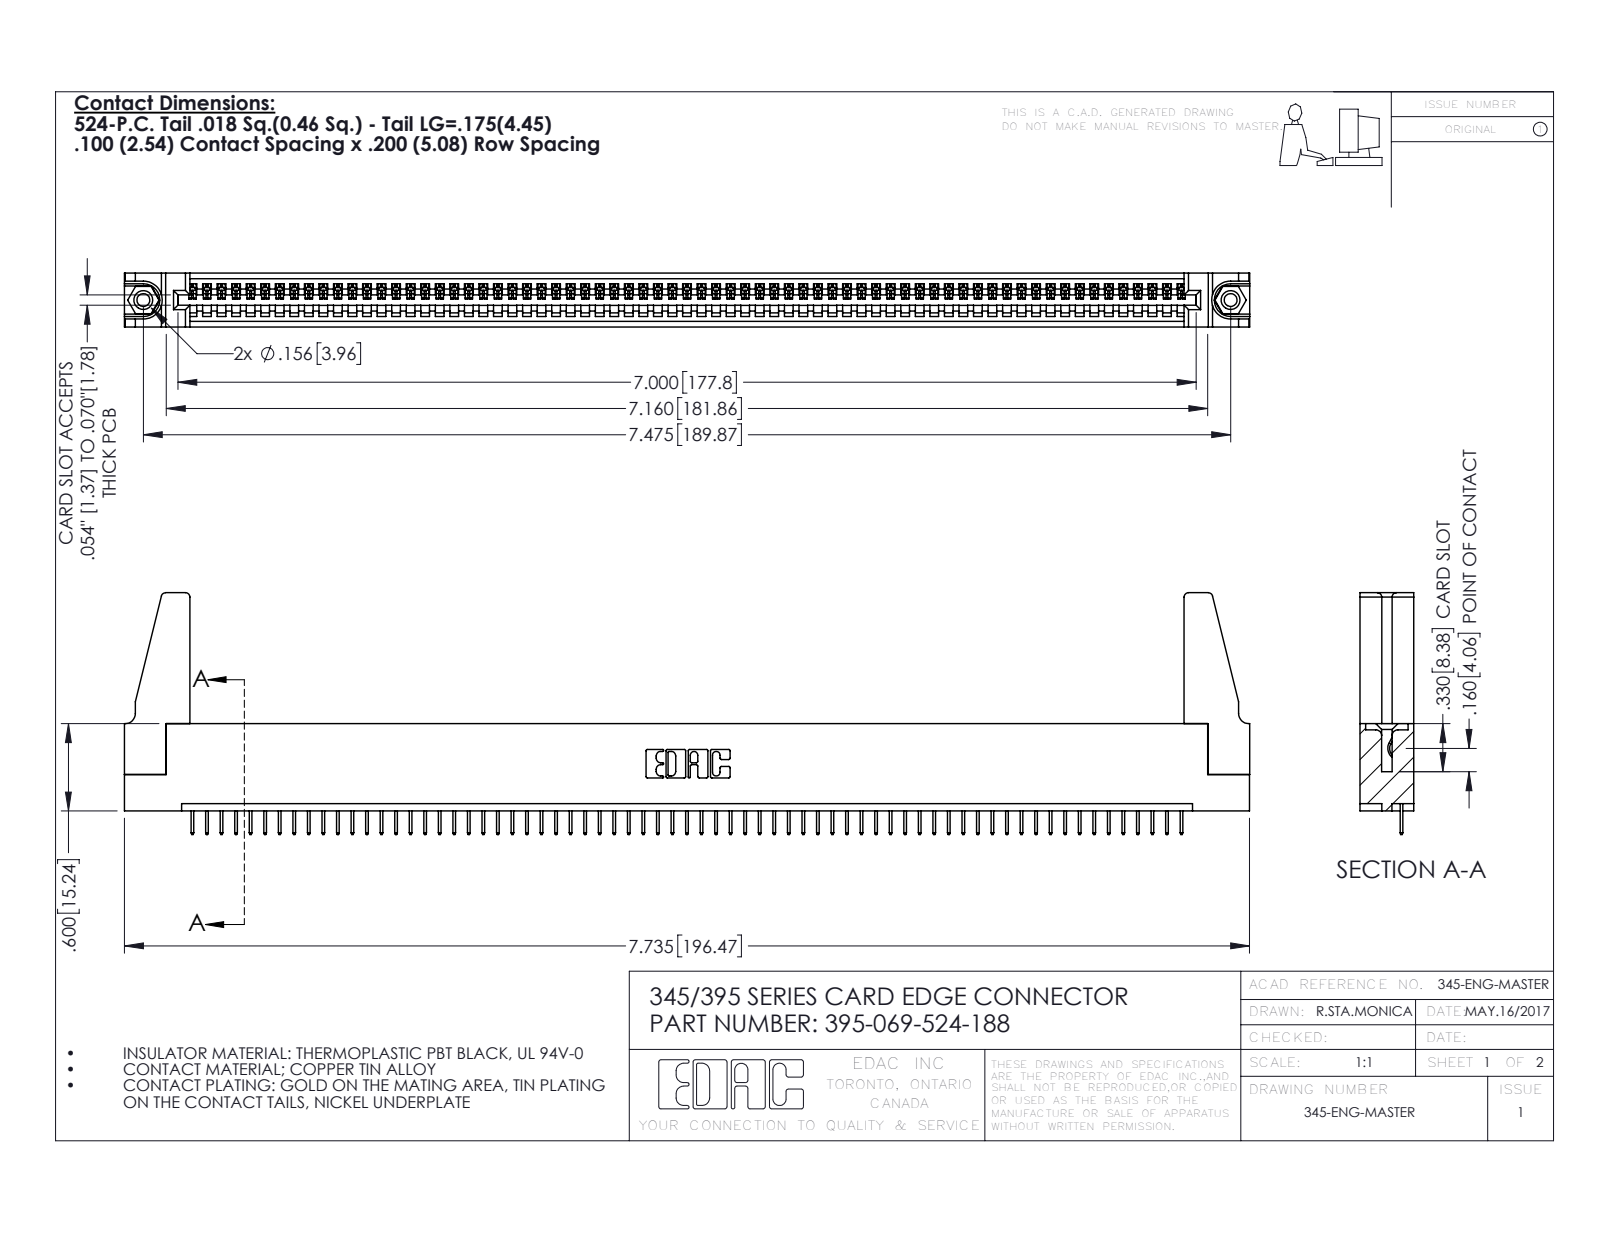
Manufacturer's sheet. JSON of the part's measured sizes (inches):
{"part_name": "345 Part_Flush Mounting Lugs - 0.156 Dia-TH; 345-220-078_345-220-088; 345-292-001_345-293-124; 345-250-001_345-250-001-102 (+1 more)", "step_written_by": "SolidWorks 2016 (CONFIG_CONTROL_DESIGN)", "units": "inches", "bodies": {"solids": 74, "faces": 4528, "planar": 3326, "cylindrical": 1186, "other": 16}, "overall_size": [7.736, 1.662, 0.37], "volume_in3": 1.334, "surface_area_in2": 42.41, "round_holes": [[0.089, 2], [0.125, 2], [0.156, 2], [0.064, 1]], "round_bosses_or_shafts": [[0.155, 2]], "partial_cylinders_radius": [[0.006, 138], [0.01, 22], [0.03, 8], [0.007, 6], [0.031, 6], [0.026, 3], [0.031, 2], [0.04, 2]], "face_to_face_distances": [0.072, 0.298, 0.37, 0.2, 0.098, 0.272, 0.025, 0.225, 0.072, 0.149], "hole_center_spacings": [0.27, 7.239, 7.475]}
